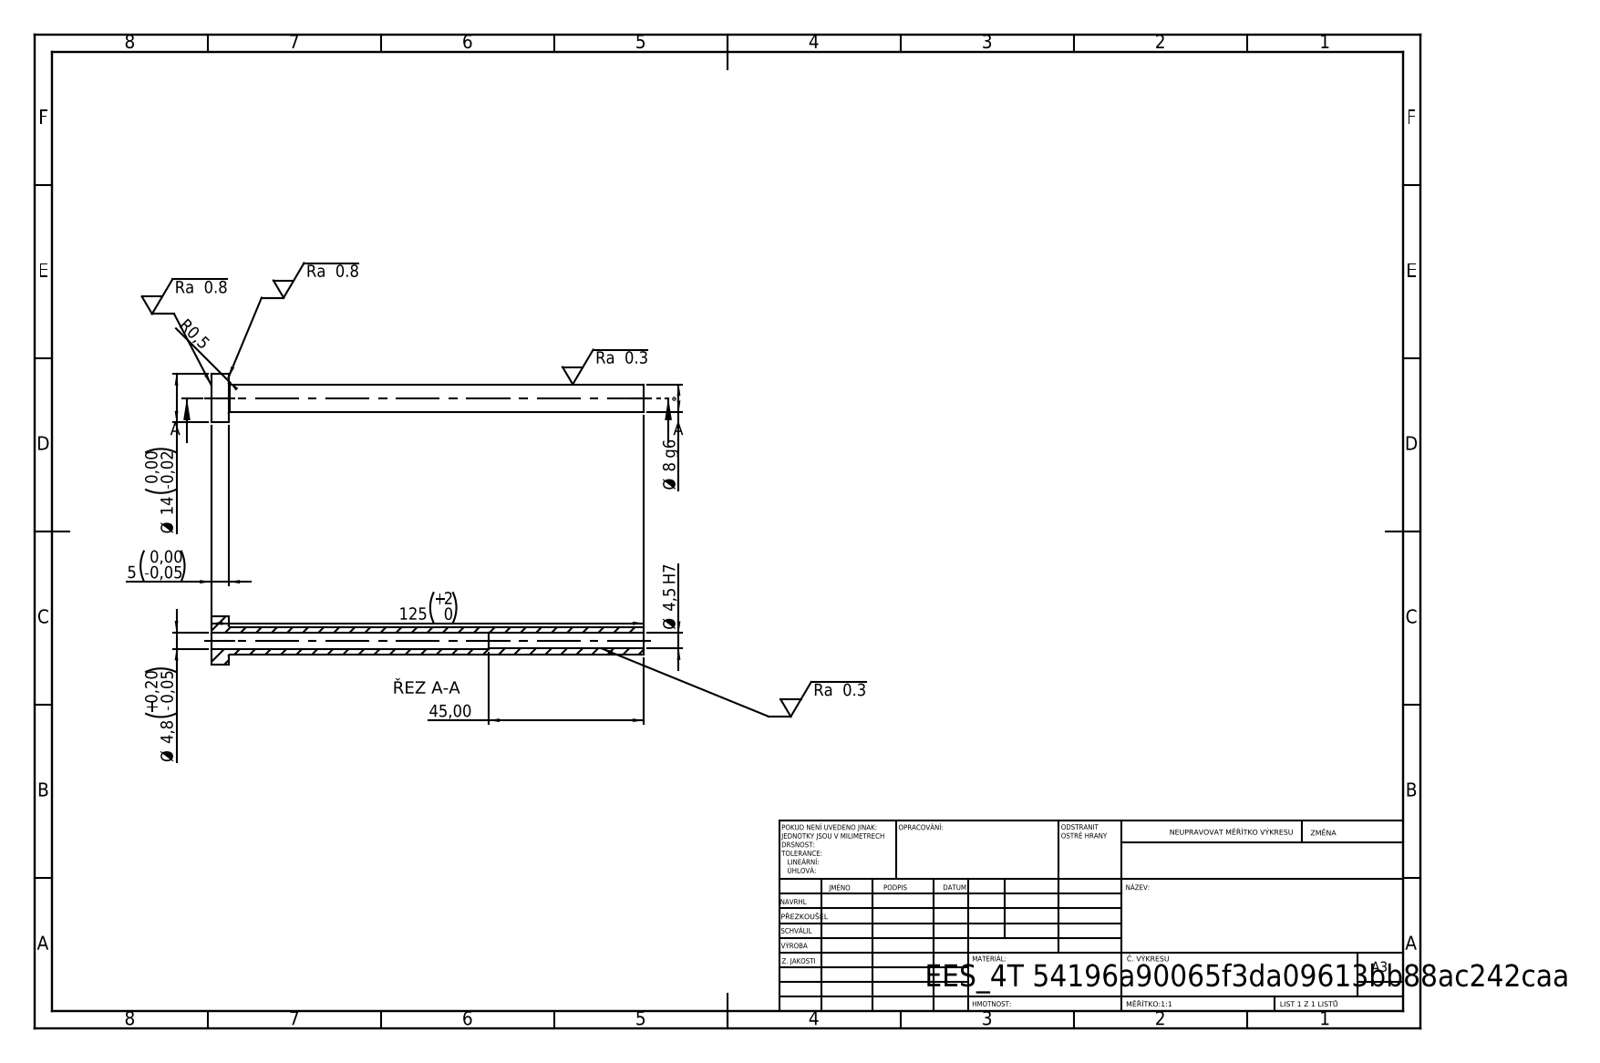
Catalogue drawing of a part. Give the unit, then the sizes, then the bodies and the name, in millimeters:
Units: millimetres
Overall size (bounding box): 125 × 14 × 14
Round holes (diameter × count): ⌀4.5 ×1, ⌀4.8 ×1
Round bosses / shafts (diameter × count): ⌀14 ×1, ⌀8 ×1
Main face-to-face distances: 5, 125, 120, 80, 75, 45
Volume: 4 640 mm³ · Surface area: 5 349 mm²
Bodies: 1 solid, 14 faces (4 planar, 8 cylindrical, 2 other)
STEP written by: SolidWorks 2019 (CONFIG_CONTROL_DESIGN)
